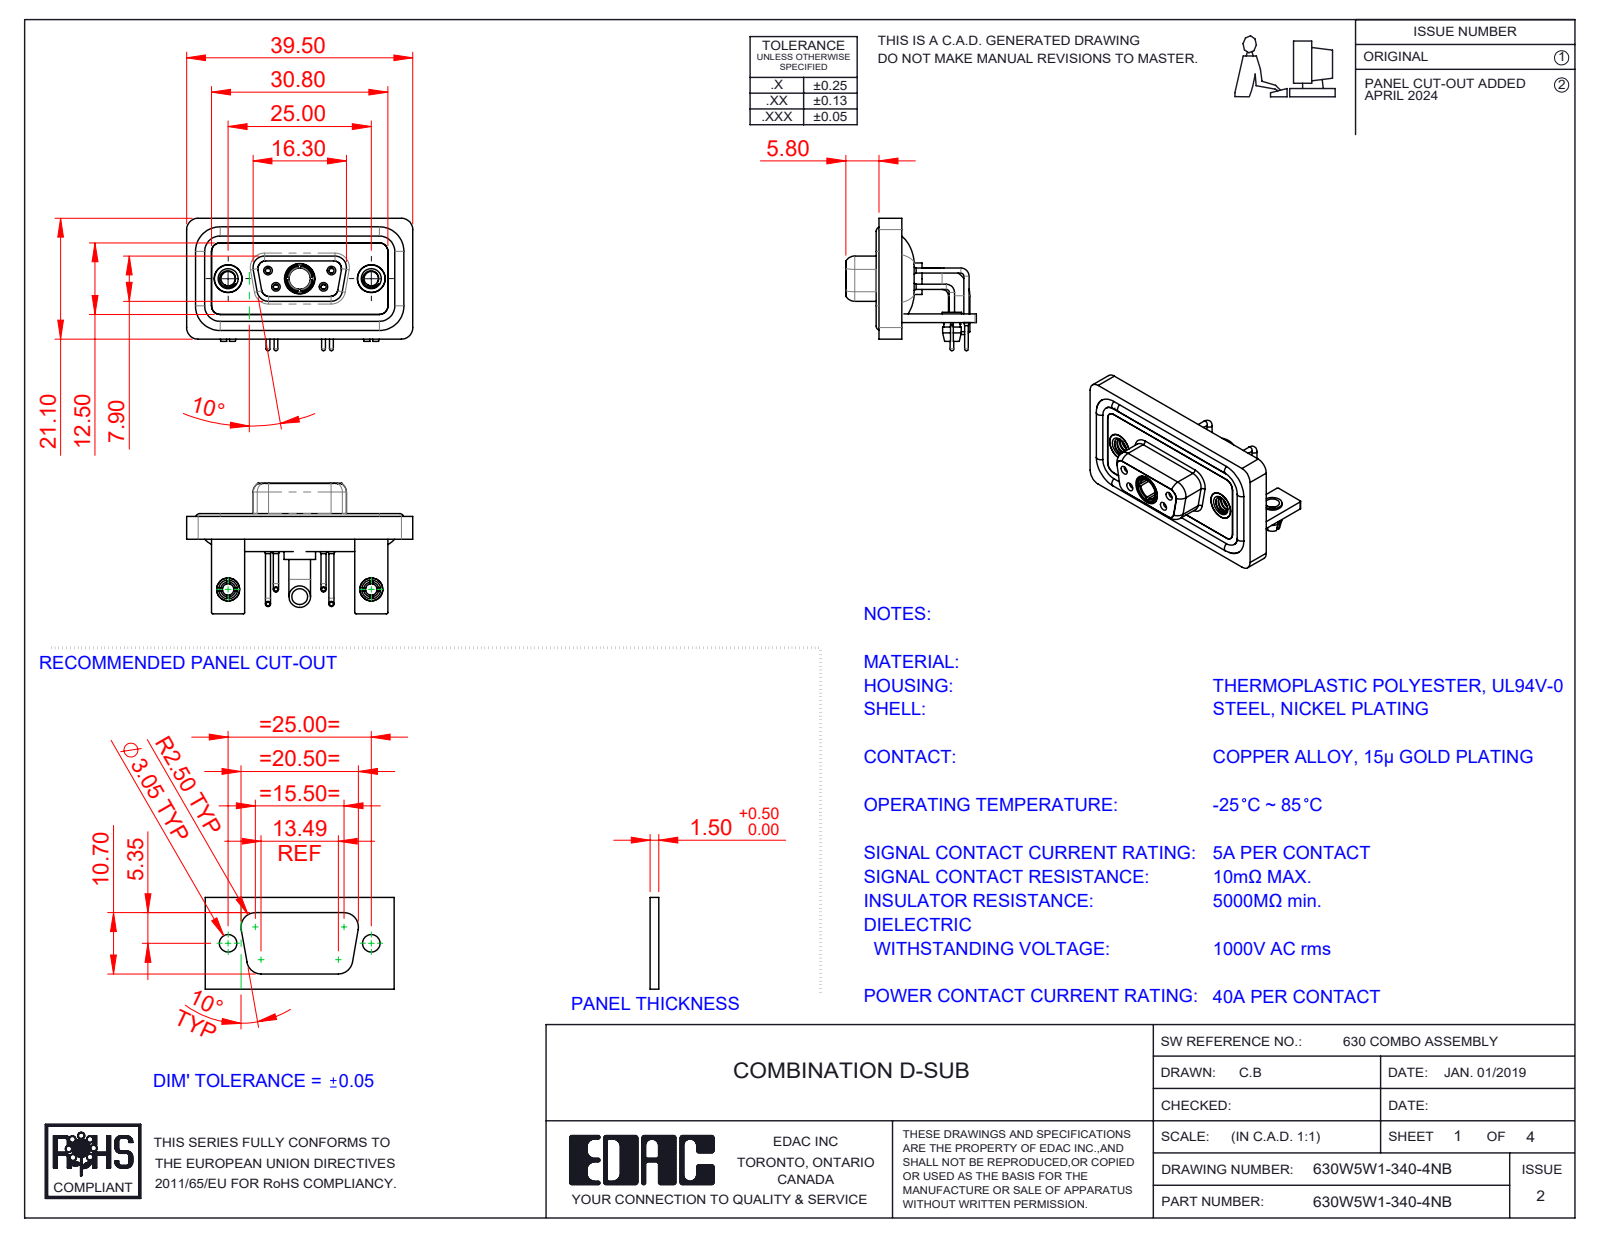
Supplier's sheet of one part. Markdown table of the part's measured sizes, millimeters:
| quantity | value |
| --- | --- |
| part name | 630Combo Contact Row 2_50 Contacts; 630Combo Shell Front_09 Contacts; 630Combo Shell Rear_09 Contacts; 630Combo Contact Row 1_50 Contacts (+7 more) |
| STEP written by | SolidWorks 2023 (CONFIG_CONTROL_DESIGN) |
| units | millimeters |
| bodies | 17 solids, 810 faces (262 planar, 359 cylindrical, 189 other) |
| overall size | 39.5 × 23.12 × 22.8 |
| volume | 5 297 mm³ |
| surface area | 8 836 mm² |
| round holes (diameter × count) | 2 × 6, 0.9 × 4, 1.1 × 4, 1.5 × 4, 2.5 × 4, 4.85 × 3, 1.6 × 2, 1.7 × 2, 3.2 × 2, 4 × 2, 4.05 × 2, 5 × 2 |
| round bosses / shafts (diameter × count) | 1.6 × 6, 0.9 × 4, 0.65 × 4, 4.95 × 2, 4.8 × 2, 4 × 2, 3.75 × 2, 3.4 × 2 |
| partial cylindrical surfaces (radius × count) | 2 × 19, 1.5 × 18, 0.25 × 16, 1.35 × 8, 1.6 × 8, 0.5 × 5, 0.6 × 4, 0.65 × 4 |
| main face-to-face distances | 0.4, 2.9, 1.5, 1.8, 1.1, 3.7, 1.6, 0.8, 2.5, 3.1 |
| hole center spacings | 3.16, 5.72, 7.1, 12.5, 18.1, 25, 4.39, 4.4 |
